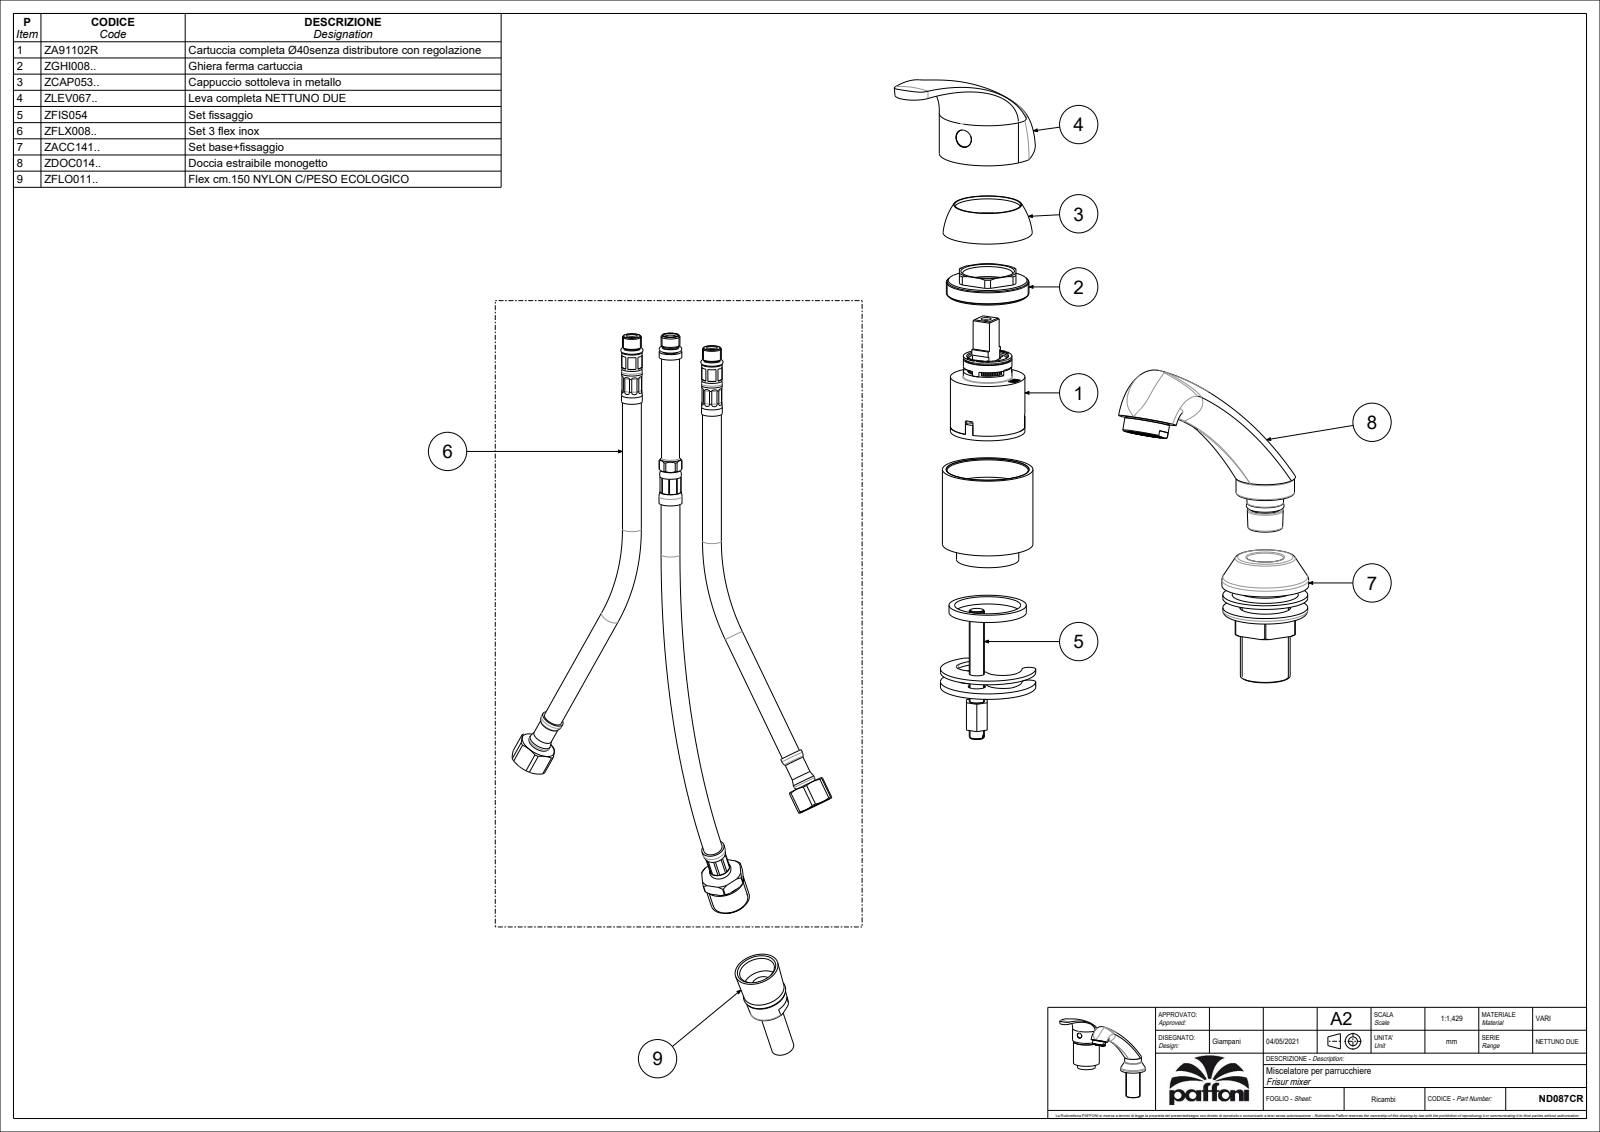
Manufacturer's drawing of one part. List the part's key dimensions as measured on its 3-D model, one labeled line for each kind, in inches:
Part name (STEP PRODUCT): ND087CR
STEP written by: CREO PARAMETRIC BY PTC INC, 2020044 (CONFIG_CONTROL_DESIGN)
Units: inches
Bodies: 2 solids, 108 faces (38 planar, 17 cylindrical, 53 other)
Overall size (bounding box): 6.481 × 5.846 × 4.348
Volume: 15.09 in³ · Surface area: 70.28 in²
Round holes (diameter × count): ⌀0.236 ×1
Round bosses / shafts (diameter × count): ⌀1.89 ×1, ⌀1.811 ×1, ⌀1.22 ×1, ⌀0.945 ×1, ⌀0.197 ×1
Partial cylindrical surfaces — rounded edges, fillets, slot ends (radius × count): R0.154 ×1, R0.157 ×1
Main face-to-face distances: 2.217, 0.303, 0.602, 2.746, 0.53, 0.713, 0.972, 1.244, 1.774, 0.138
